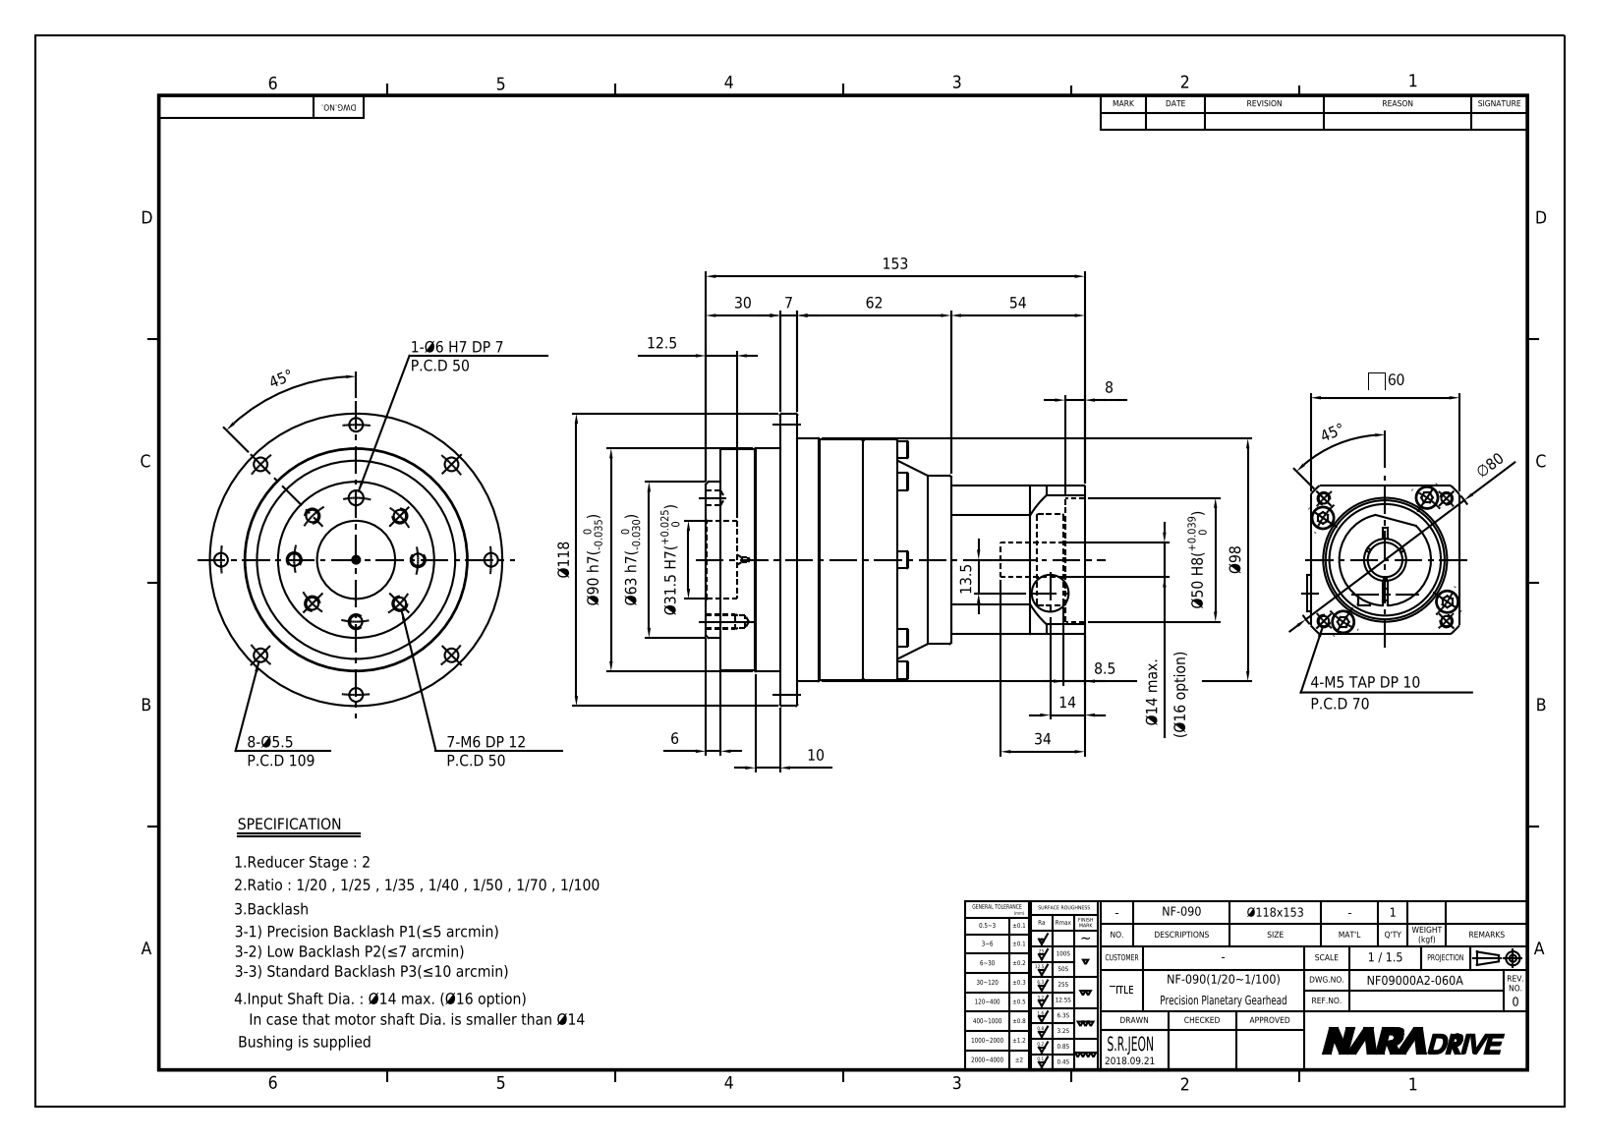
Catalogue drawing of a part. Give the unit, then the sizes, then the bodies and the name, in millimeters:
Units: millimetres
Overall size (bounding box): 153 × 118 × 118
Round holes (diameter × count): ⌀5.5 ×13, ⌀3.24 ×12, ⌀4.92 ×7, ⌀4.13 ×4, ⌀4.2 ×4, ⌀7.5 ×4, ⌀9 ×4, ⌀2 ×1, ⌀6 ×1, ⌀7 ×1, ⌀8.5 ×1, ⌀14 ×1
Round bosses / shafts (diameter × count): ⌀8.5 ×13, ⌀5 ×5, ⌀118 ×1, ⌀98 ×1, ⌀97 ×1, ⌀90 ×1, ⌀89.5 ×1, ⌀85 ×1
Partial cylindrical surfaces — rounded edges, fillets, slot ends (radius × count): R0.5 ×4, R2.07 ×1, R4.5 ×1, R35 ×1, R40 ×1
Main face-to-face distances: 33.5, 7, 26.5, 12, 45.5, 24, 31, 57.5, 91.8, 67.8
Hole centre spacings: 77.07, 30.25, 54.5, 25, 39.09, 48.75, 21.69, 35
Volume: 522 341 mm³ · Surface area: 116 031 mm²
Bodies: 2 solids, 422 faces (205 planar, 113 cylindrical, 104 other)
Part name (STEP PRODUCT): NF09000A2-060A
STEP written by: Autodesk Inventor 2015 (AUTOMOTIVE_DESIGN)
